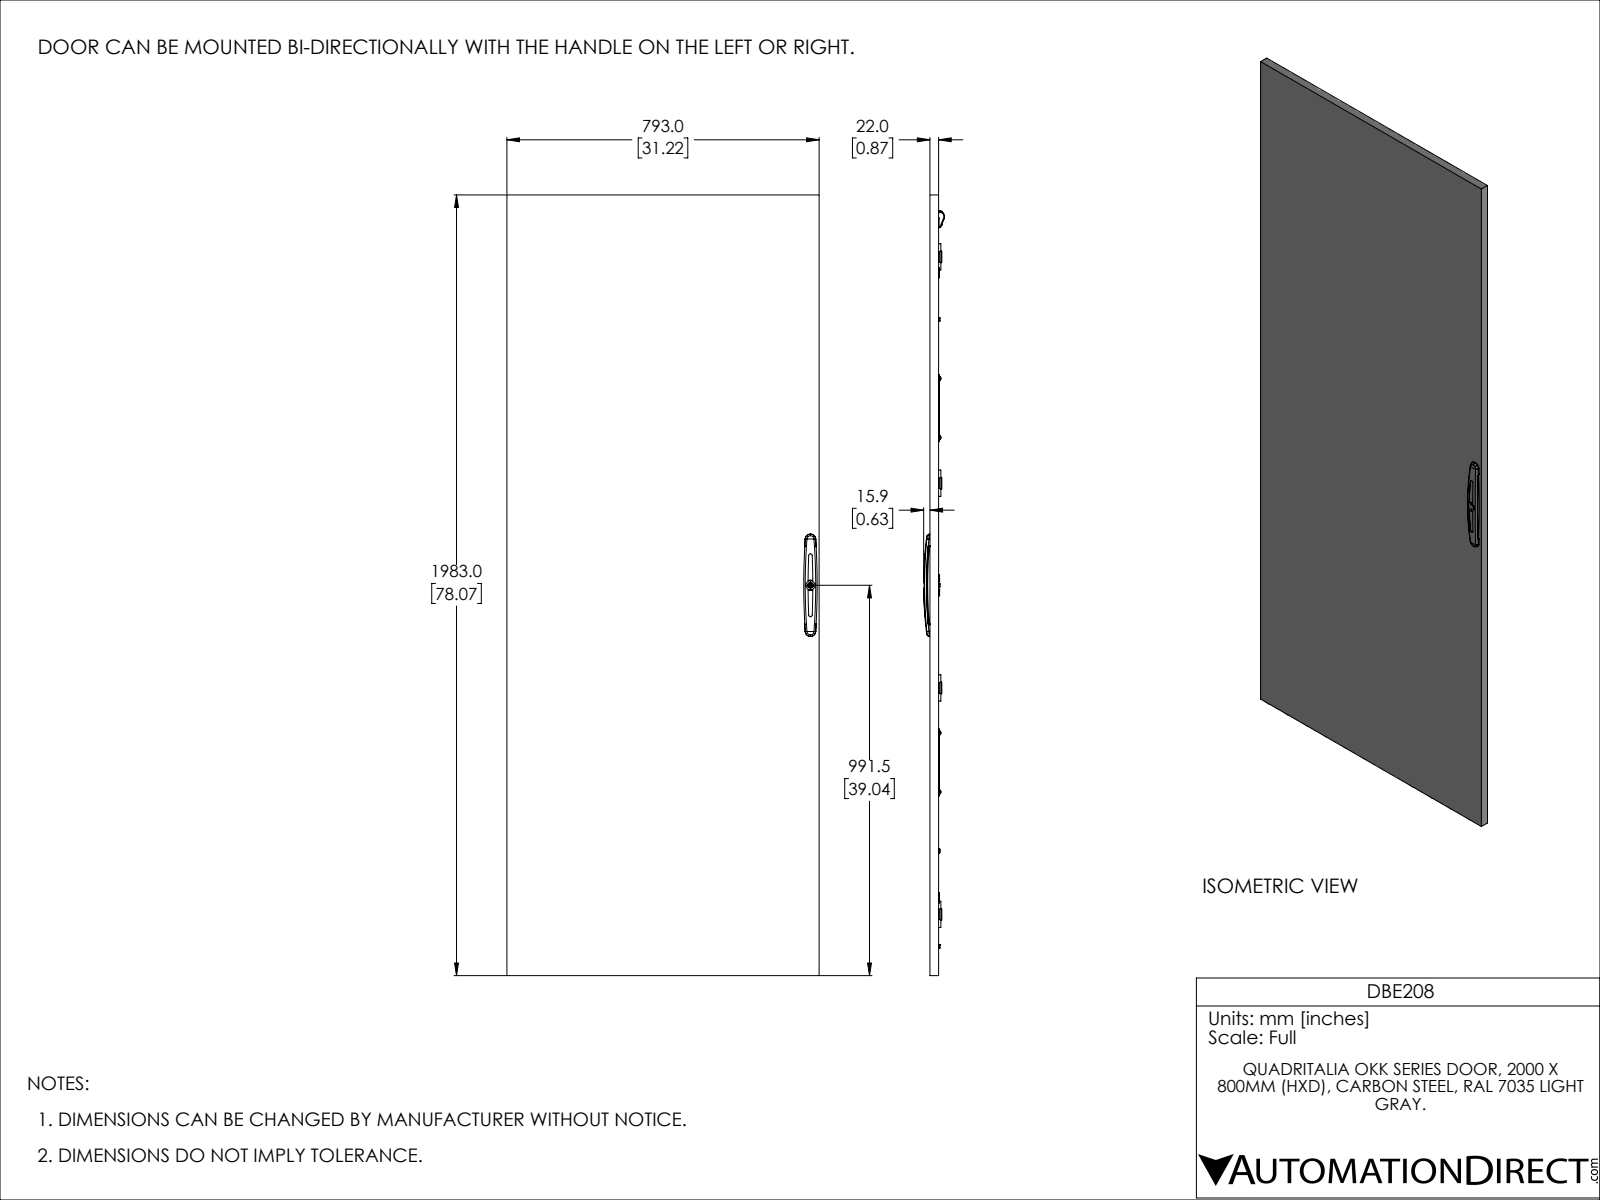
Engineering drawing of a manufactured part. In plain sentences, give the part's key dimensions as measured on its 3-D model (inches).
The part is named "DBE208". Its 3-D file was written by "SolidWorks 2021 (CONFIG_CONTROL_DESIGN)". It is 91 solids with 3383 faces: 1627 planar, 1186 cylindrical and 570 other. Overall it measures 78.071 by 31.22 by 2.091 inches. Its volume is 287.3 cubic inches and its surface area 7 137 square inches. Round holes: 144 of diameter 0.167, 29 of diameter 0.315, 18 of diameter 0.354, 10 of diameter 0.194, 8 of diameter 0.01, 8 of diameter 0.197, 4 of diameter 0.244, 4 of diameter 0.276, 3 of diameter 0.205, 2 of diameter 0.134, 2 of diameter 0.169, 2 of diameter 0.173. Round bosses or shafts: 21 of diameter 0.276, 17 of diameter 0.236, 10 of diameter 0.394, 10 of diameter 0.283, 9 of diameter 0.197, 8 of diameter 0.193, 2 of diameter 0.315, 2 of diameter 0.157. Partial cylindrical surfaces (rounded edges, fillets, slot ends): 74 of radius 0.012, 70 of radius 0.039, 36 of radius 0.059, 33 of radius 0.02, 28 of radius 0.098, 16 of radius 0.177, 15 of radius 0.079, 8 of radius 0.016. The main face-to-face distances are 0.079, 0.059, 0.728, 0.787, 0.669, 25.984, 0.866, 0.138, 0.807, 31.142. The hole center spacings are 0.984, 1.969, 2.953, 3.937, 4.921, 8.858, 5.906, 6.89.
